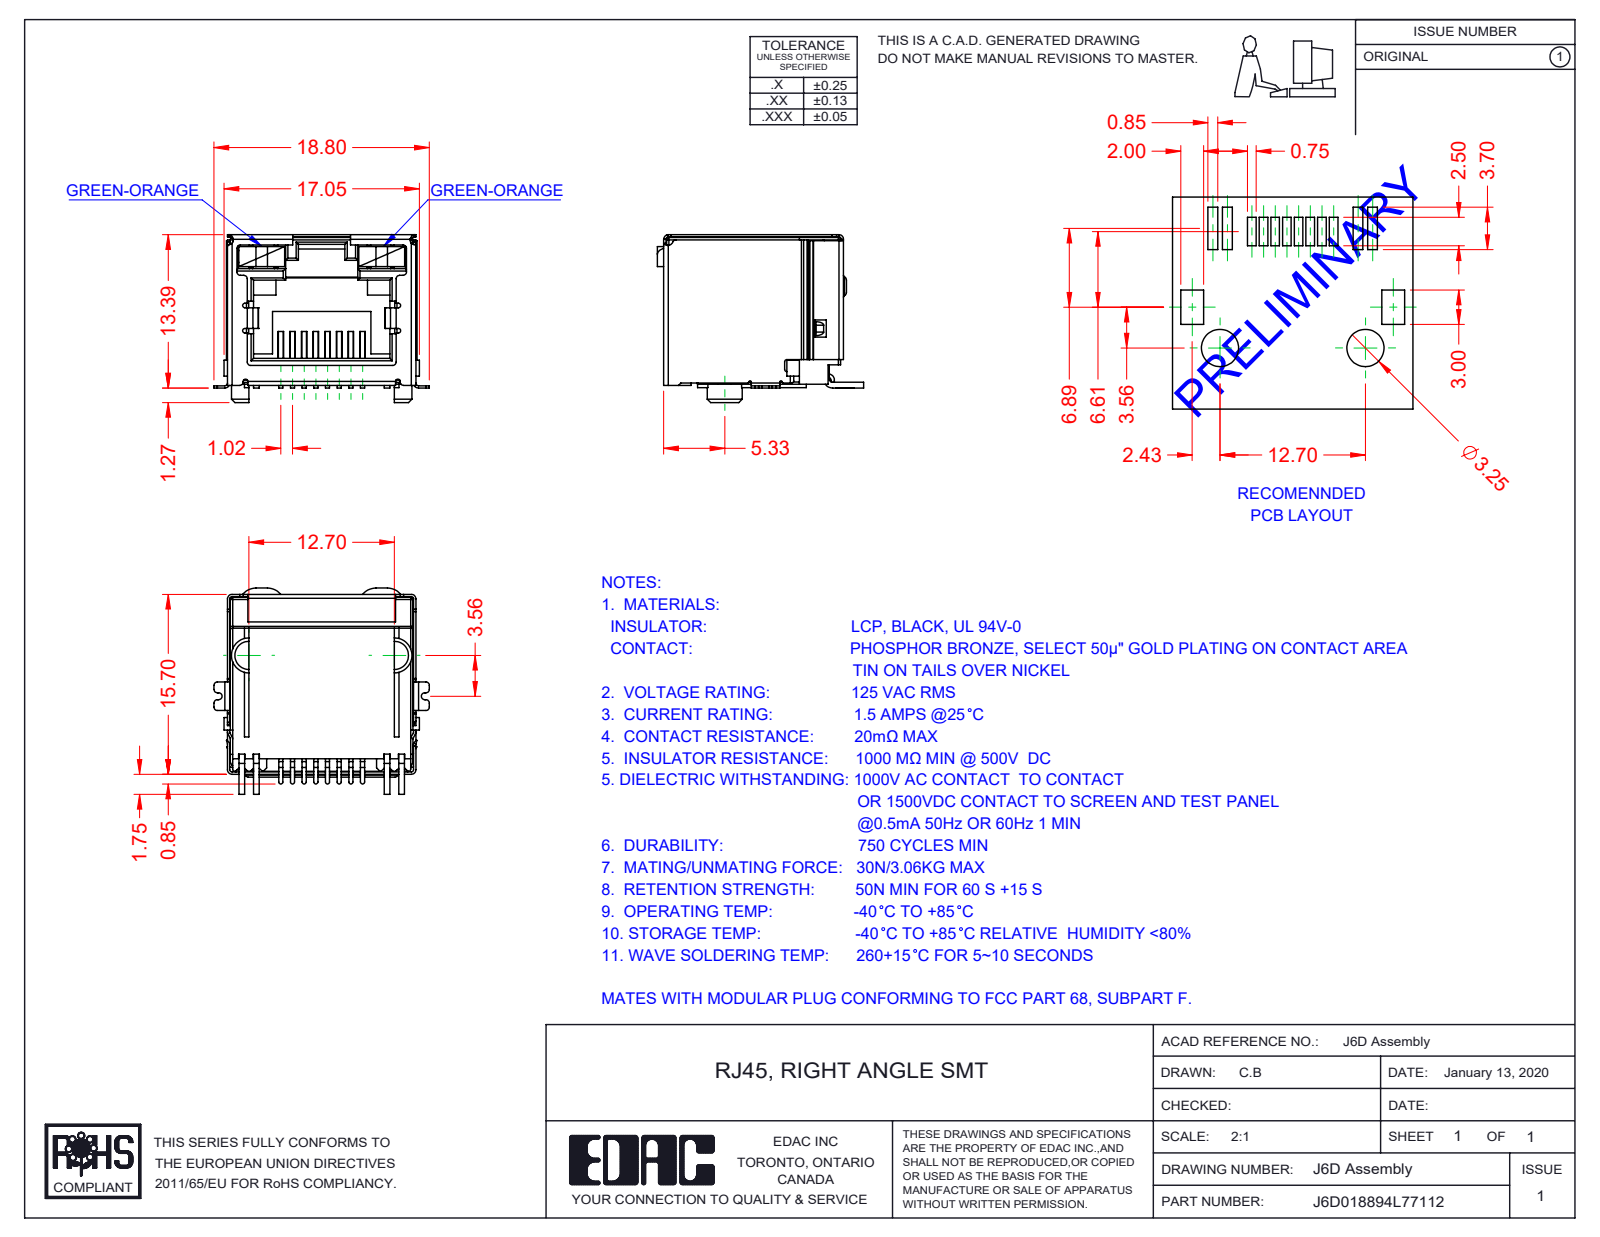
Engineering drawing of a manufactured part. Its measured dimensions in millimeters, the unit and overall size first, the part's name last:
Units: millimetres
Overall size (bounding box): 18.8 × 18 × 14.65
Partial cylindrical surfaces — rounded edges, fillets, slot ends (radius × count): R0.3 ×39, R0.2 ×37, R0.4 ×16, R0.1 ×12, R0.15 ×8, R0.18 ×8, R0.5 ×6, R1.5 ×5
Main face-to-face distances: 16, 16.25, 16.2, 2.25, 1, 15.95, 16.05, 12.8, 0.45, 16.45
Volume: 1 804 mm³ · Surface area: 4 898 mm²
Bodies: 12 solids, 899 faces (646 planar, 220 cylindrical, 33 other)
Part name (STEP PRODUCT): J6D018894L77112; 6D LED LH_7-Green-Orange; 6D Contacts; 6D Shield_LED - No EMI (+2 more)
STEP written by: SolidWorks 2016 (CONFIG_CONTROL_DESIGN)
